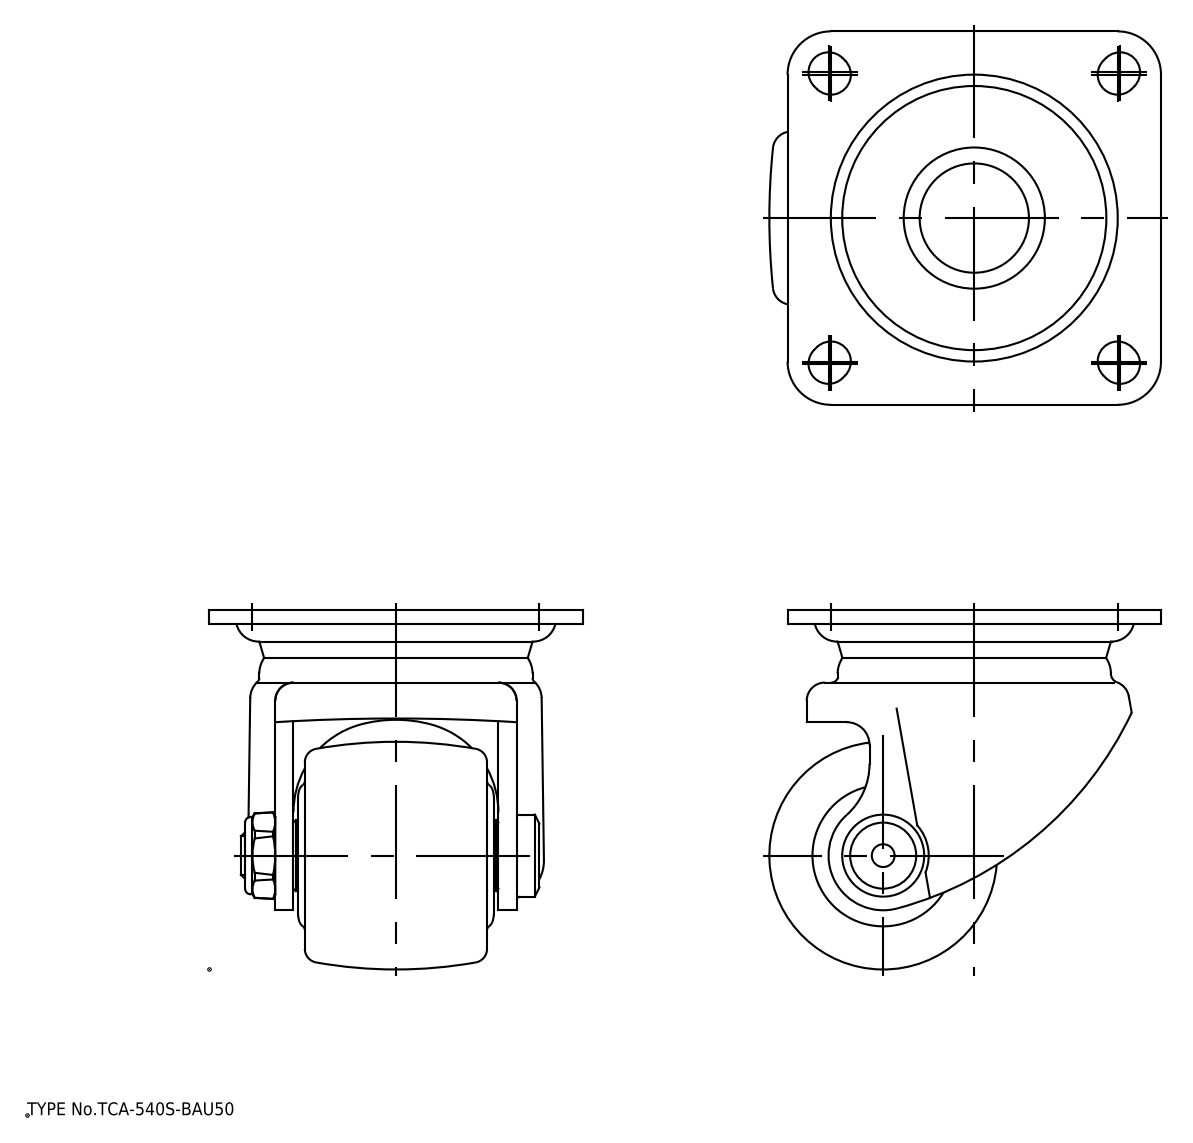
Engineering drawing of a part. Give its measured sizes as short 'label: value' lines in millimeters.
name: plate; wheel
written by: spGate 19.8.4 (****-****-****-****) (AUTOMOTIVE_DESIGN)
unit: mm
bodies: 3 solids, 180 faces (41 planar, 63 cylindrical, 76 other)
size: 86 × 82 × 79
volume: 172 850 mm³; area: 48 597 mm²
holes: 4× ⌀8.8, 1× ⌀10.2, 1× ⌀23, 1× ⌀24, 1× ⌀26.47, 1× ⌀31, 1× ⌀54.3, 1× ⌀63
bosses: 1× ⌀60, 1× ⌀58, 1× ⌀18, 1× ⌀17, 1× ⌀15.6, 1× ⌀10
rounds: 4× R9.5, 3× R5, 2× R2, 1× R6, 1× R9.1, 1× R12, 1× R15, 1× R31.5
face distances: 7, 3.8, 3.2, 20, 13, 16.8, 42.5, 4, 2.5, 5
hole spacings: 44.55, 63, 41.16, 48.21, 89.1, 5
